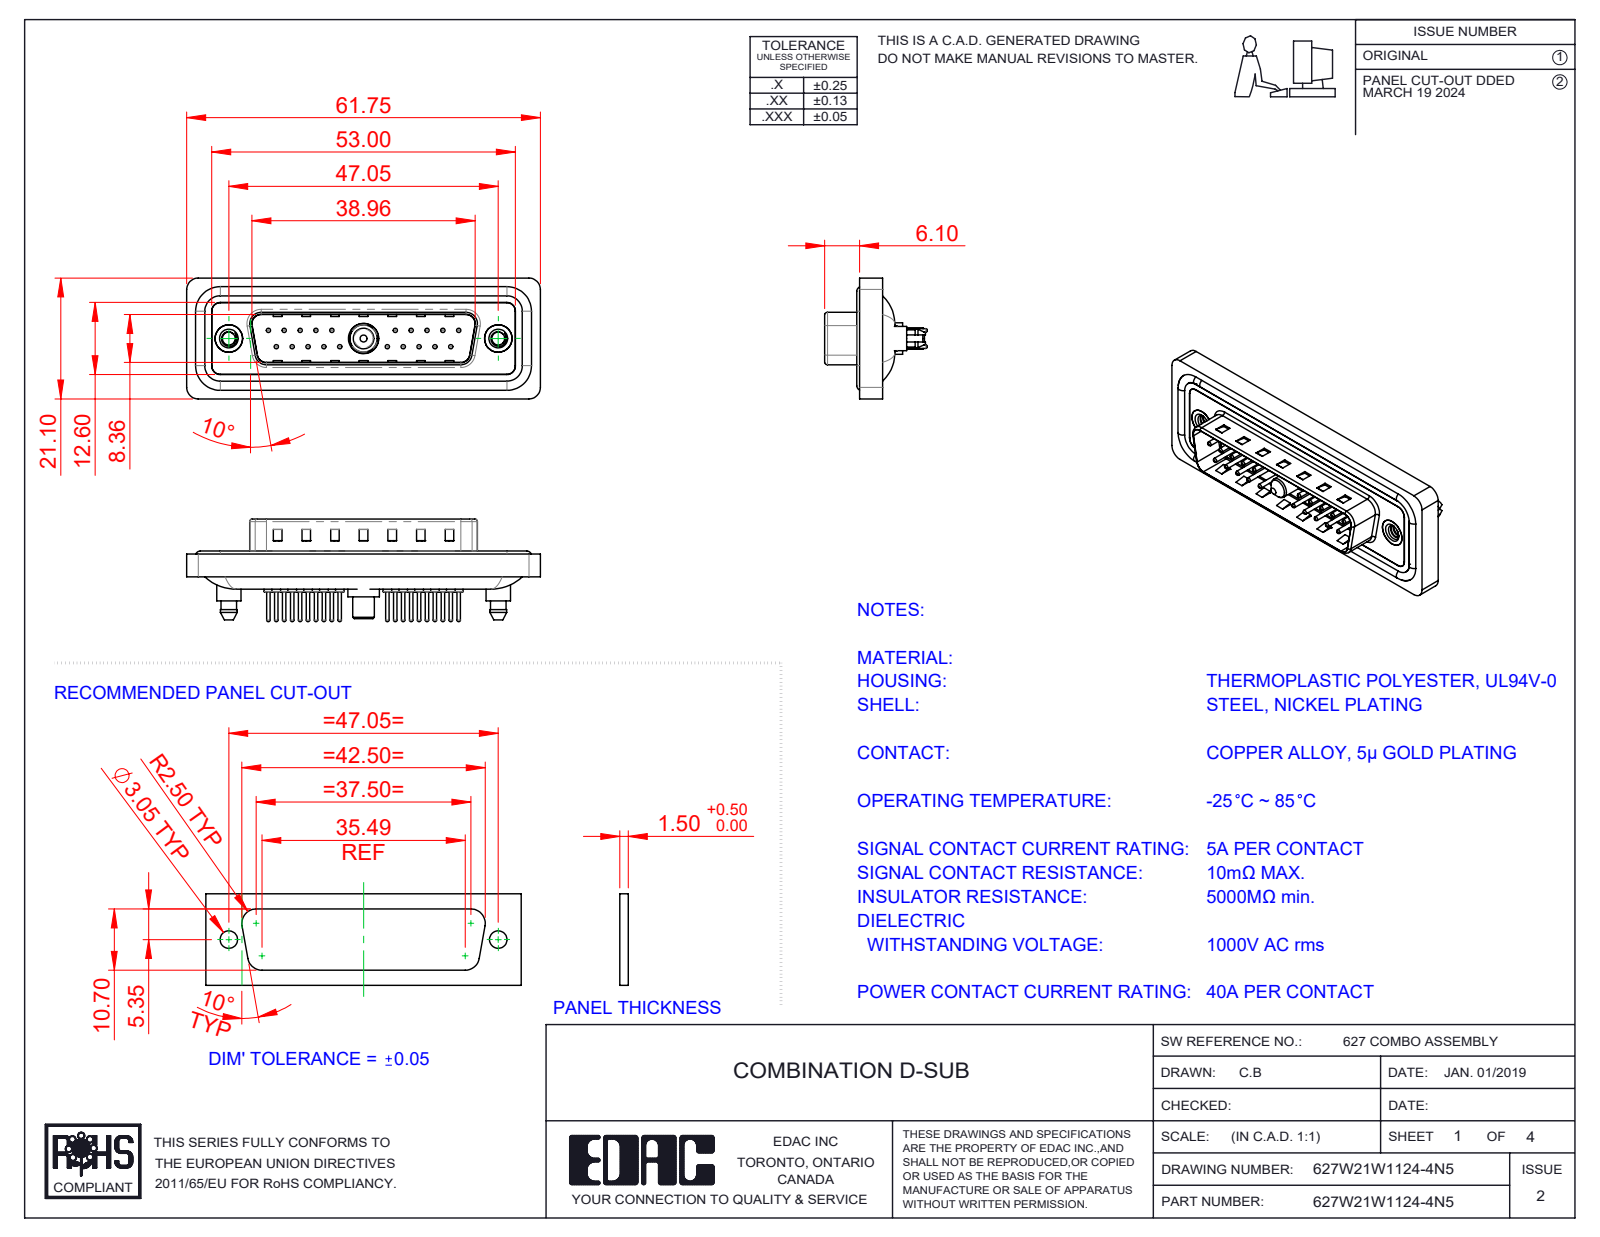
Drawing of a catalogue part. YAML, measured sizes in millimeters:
part_name: "627W21W1124-4N5; 627Combo Threaded Boardlock_5; 627Combo Contact Row 2_24; Power Pin_40A S (+5 more)"
step_written_by: "SolidWorks 2023 (CONFIG_CONTROL_DESIGN)"
units: millimeters
bodies: {solids: 29, faces: 1312, planar: 375, cylindrical: 519, other: 418}
overall_size: [61.75, 21.1, 17.9]
volume: 7350
surface_area: 12297
round_holes:
  - {diameter: 0.75, count: 20}
  - {diameter: 1.6, count: 20}
  - {diameter: 2, count: 20}
  - {diameter: 2.26, count: 2}
  - {diameter: 4, count: 2}
  - {diameter: 4.8, count: 2}
  - {diameter: 5, count: 2}
  - {diameter: 4.85, count: 1}
  - {diameter: 5.3, count: 1}
round_bosses_or_shafts:
  - {diameter: 1.5, count: 20}
  - {diameter: 0.6, count: 20}
  - {diameter: 1.6, count: 4}
  - {diameter: 5.4, count: 2}
  - {diameter: 4.9, count: 2}
  - {diameter: 4.25, count: 2}
  - {diameter: 5.5, count: 1}
  - {diameter: 5.2, count: 1}
partial_cylinders:
  - {radius: 1.5, count: 24}
  - {radius: 2, count: 18}
  - {radius: 1.6, count: 10}
  - {radius: 0.5, count: 8}
  - {radius: 0.25, count: 4}
  - {radius: 0.6, count: 4}
  - {radius: 0.65, count: 4}
  - {radius: 0.9, count: 4}
face_to_face_distances: [0.4, 1.5, 1.1, 1.6, 3.1, 0.5, 2.9, 4.1, 0.82, 9.58]
hole_center_spacings: [3.16, 2.77, 5.54, 8.31, 5.04, 19.39, 20.97, 22.16]
